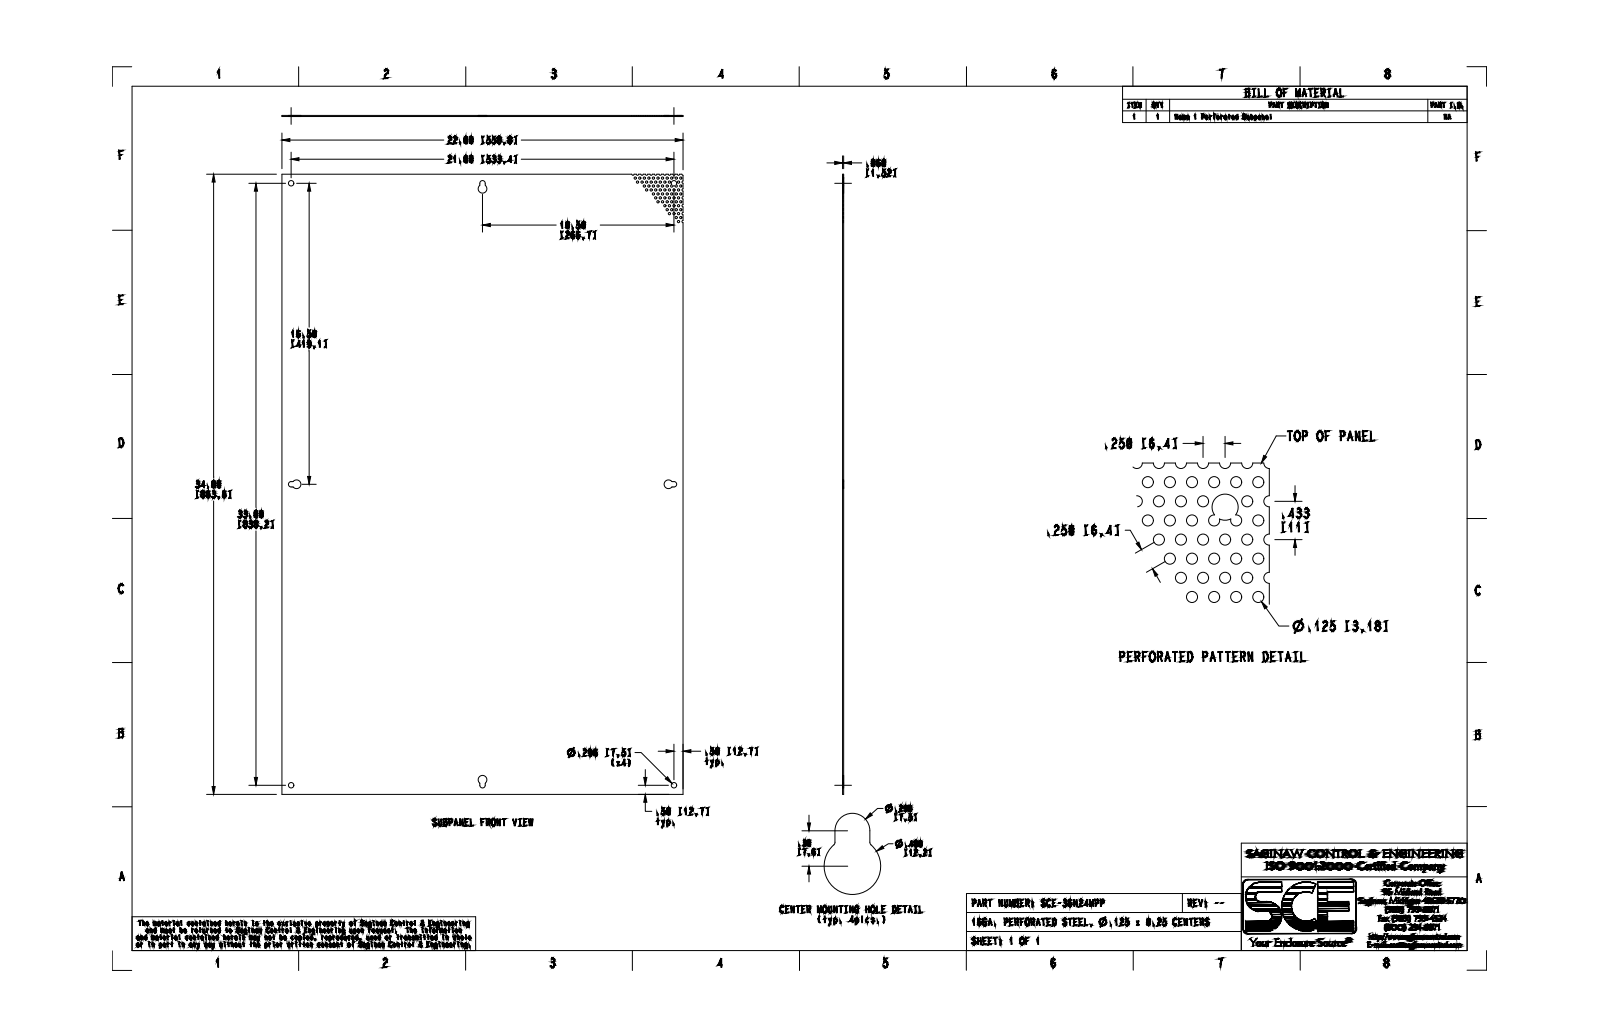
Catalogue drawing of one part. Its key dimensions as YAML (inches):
part_name: "SCE-36N24MPP"
step_written_by: "SolidWorks 2019 (CONFIG_CONTROL_DESIGN)"
units: inches
bodies: {solids: 1, faces: 140, planar: 31, cylindrical: 109, other: 0}
overall_size: [34, 22, 0.06]
volume: 44.75
surface_area: 1501
round_holes:
  - {diameter: 0.125, count: 45}
  - {diameter: 0.125, count: 25}
  - {diameter: 0.296, count: 4}
partial_cylinders:
  - {radius: 0.063, count: 11}
  - {radius: 0.03, count: 8}
  - {radius: 0.062, count: 7}
  - {radius: 0.148, count: 4}
  - {radius: 0.24, count: 4}
face_to_face_distances: [0.06, 22, 34, 16.852, 17.148, 0.296, 10.852, 11.148]
hole_center_spacings: [0.25, 0.661, 0.5, 0.433, 1.323, 0.433, 1.09, 0.75]
